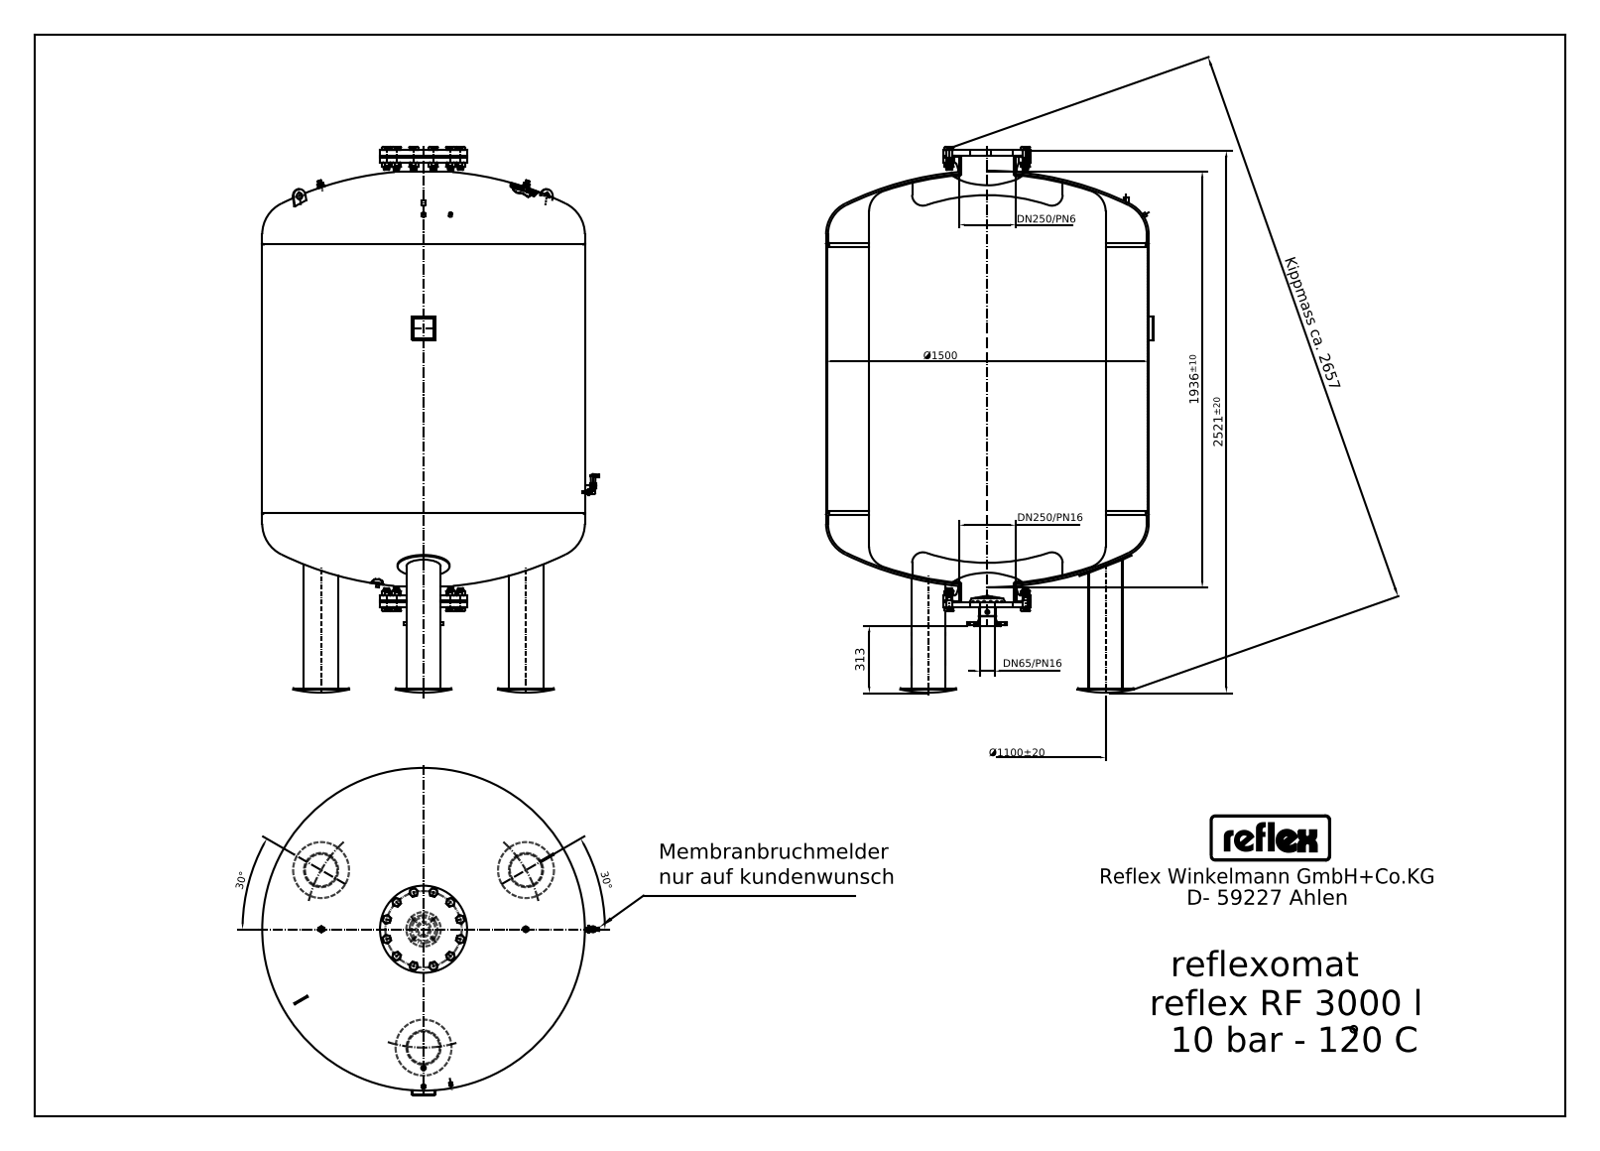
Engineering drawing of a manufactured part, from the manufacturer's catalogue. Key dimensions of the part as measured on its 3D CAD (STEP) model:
STEP written by: Mechanical Desktop 2009 (CONFIG_CONTROL_DESIGN)
Units: millimetres
Bodies: 23 solids, 889 faces (514 planar, 207 cylindrical, 168 other)
Overall size (bounding box): 2516 × 1566 × 1520
Volume: 3 108 000 000 mm³ · Surface area: 20 470 000 mm²
Round holes (diameter × count): ⌀11.45 ×2, ⌀3.5 ×1, ⌀14.95 ×1, ⌀30 ×1, ⌀260.4 ×1
Round bosses / shafts (diameter × count): ⌀16 ×12, ⌀159 ×3, ⌀21.3 ×3, ⌀18.5 ×3, ⌀28 ×2, ⌀20 ×2, ⌀1500 ×1, ⌀375 ×1
Partial cylindrical surfaces — rounded edges, fillets, slot ends (radius × count): R1 ×5, R8.44 ×4, R3.38 ×3, R6 ×3, R2 ×2, R3 ×2, R5.76 ×2, R10.12 ×2
Main face-to-face distances: 1276, 22, 2093, 27, 2066, 1665, 389, 1687, 411, 428
Hole centre spacings: 645, 769.5, 1004.07
